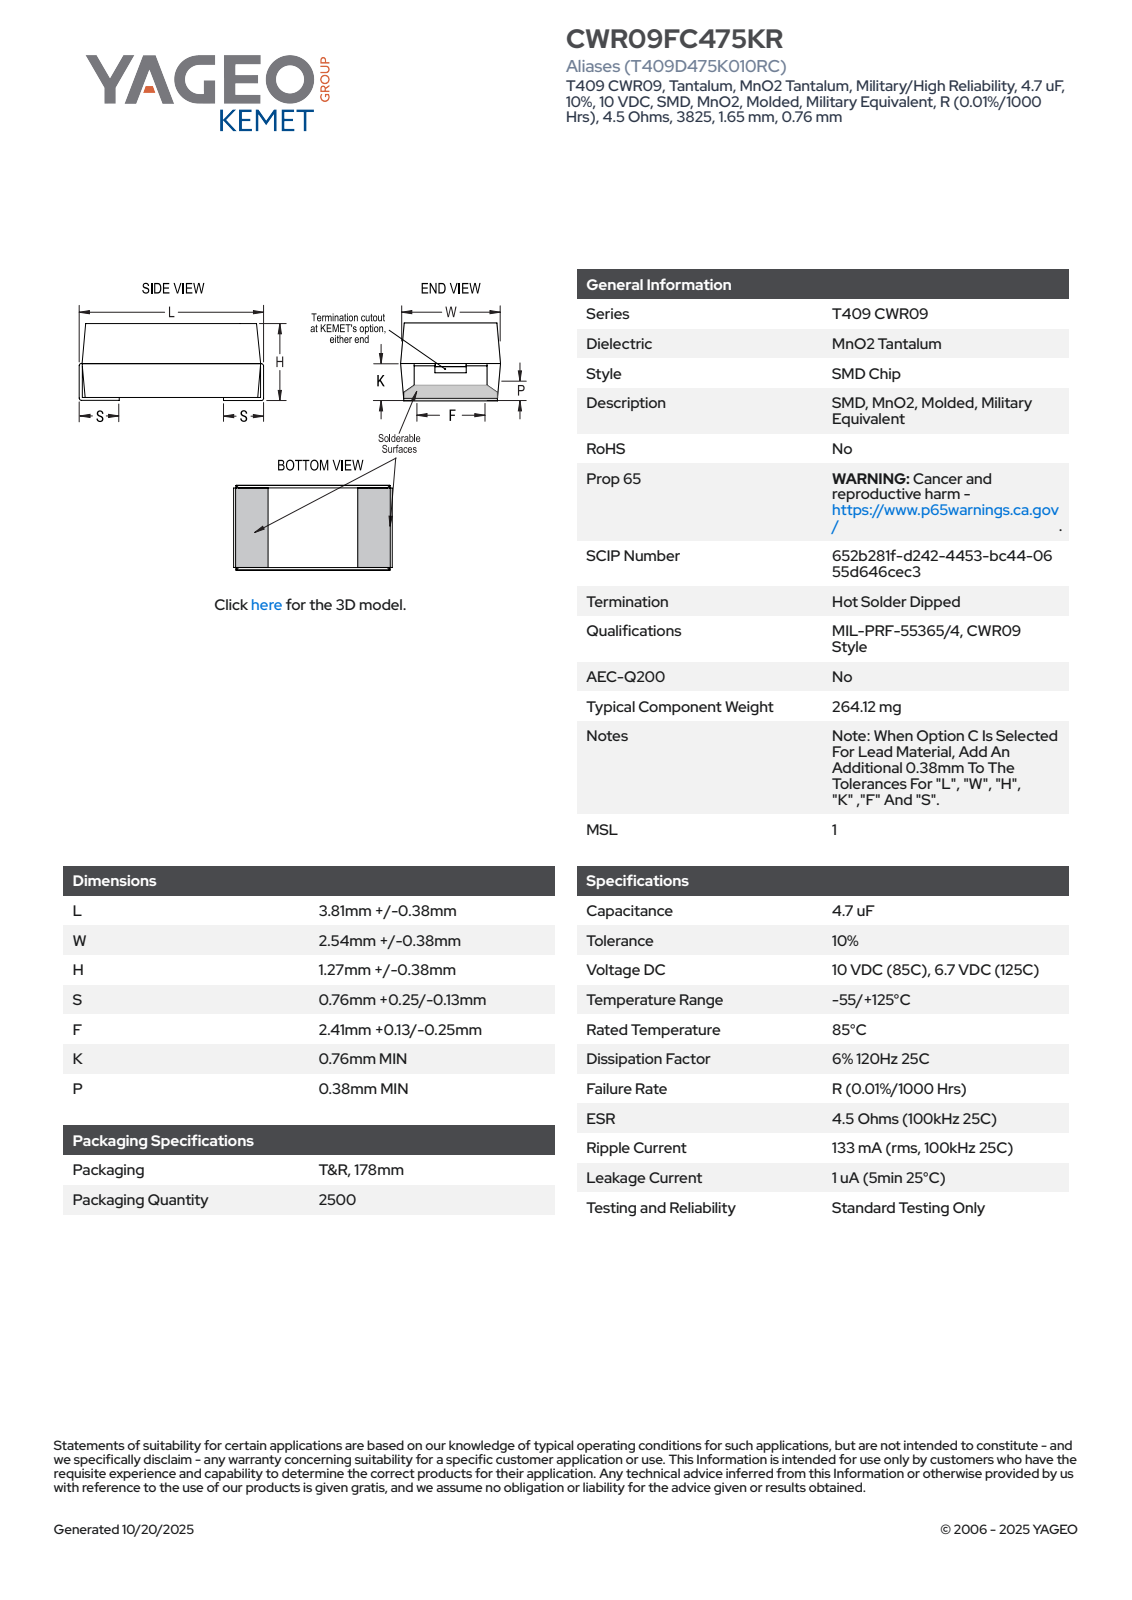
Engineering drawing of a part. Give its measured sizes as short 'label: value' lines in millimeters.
name: CTS_TCM3M_3825_L4.19H1.65S0.76F2.54K0.76P0.38W2.92
written by: SolidWorks 2014 (AUTOMOTIVE_DESIGN)
unit: mm
bodies: 4 solids, 85 faces (81 planar, 4 cylindrical, 0 other)
size: 4.19 × 2.92 × 1.75
volume: 18 mm³; area: 54 mm²
rounds: 4× R0.1
face distances: 1.65, 4.09, 1.75, 3.99, 4.19, 0.76, 3.43, 0.66, 3.33, 2.54
